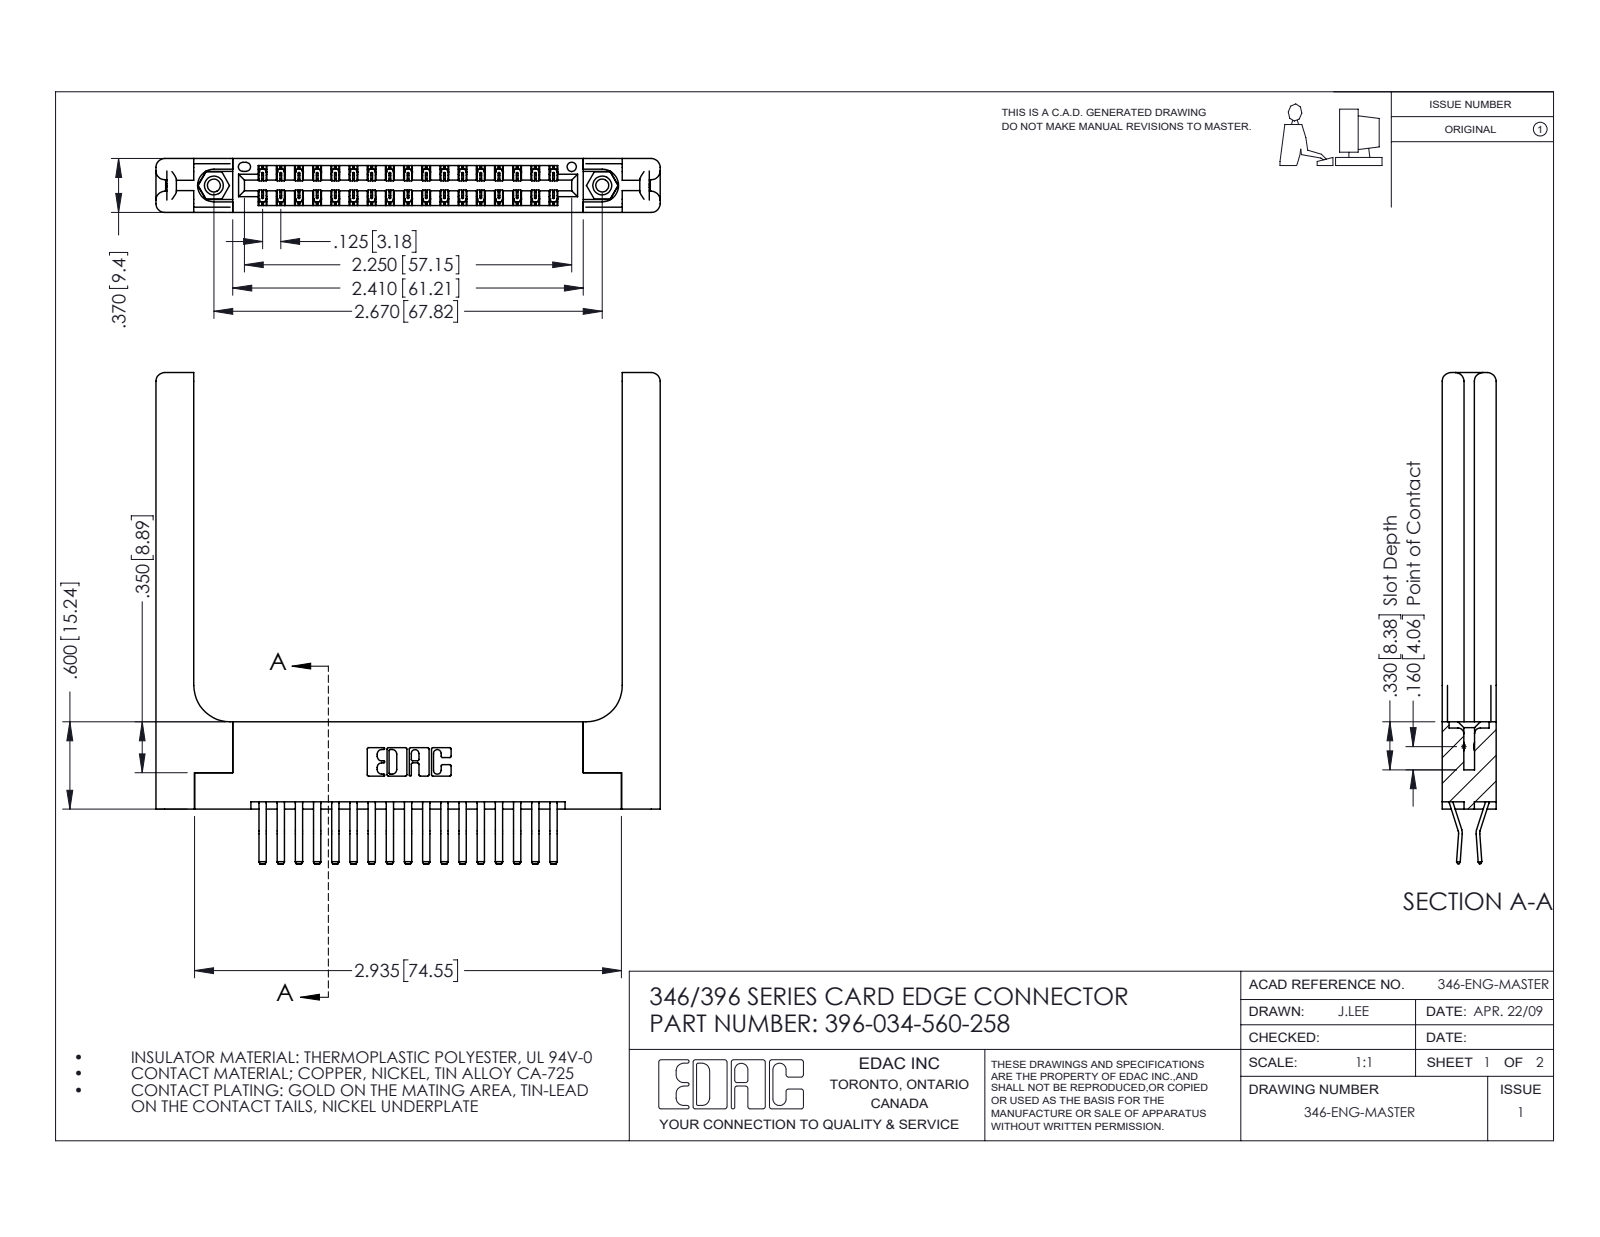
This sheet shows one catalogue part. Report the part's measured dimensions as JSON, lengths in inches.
{"part_name": "396-034-560-258; 346-220-058_345-220-058; 345-250-001_345-250-001-102; 345-292-001_560 Tail (+1 more)", "step_written_by": "SolidWorks 2016 (CONFIG_CONTROL_DESIGN)", "units": "inches", "bodies": {"solids": 39, "faces": 2214, "planar": 1414, "cylindrical": 740, "other": 60}, "overall_size": [3.466, 3.375, 0.37], "volume_in3": 0.983, "surface_area_in2": 26.37, "round_holes": [[0.089, 2], [0.125, 2], [0.156, 2], [0.064, 1]], "round_bosses_or_shafts": [[0.155, 2]], "partial_cylinders_radius": [[0.006, 51], [0.01, 22], [0.06, 16], [0.007, 6], [0.031, 6], [0.026, 3], [0.01, 2], [0.014, 2]], "face_to_face_distances": [0.37, 0.15, 0.072, 0.148, 0.048, 0.322, 0.25, 0.025, 0.102, 0.22], "hole_center_spacings": [0.246, 2.463, 2.67]}
